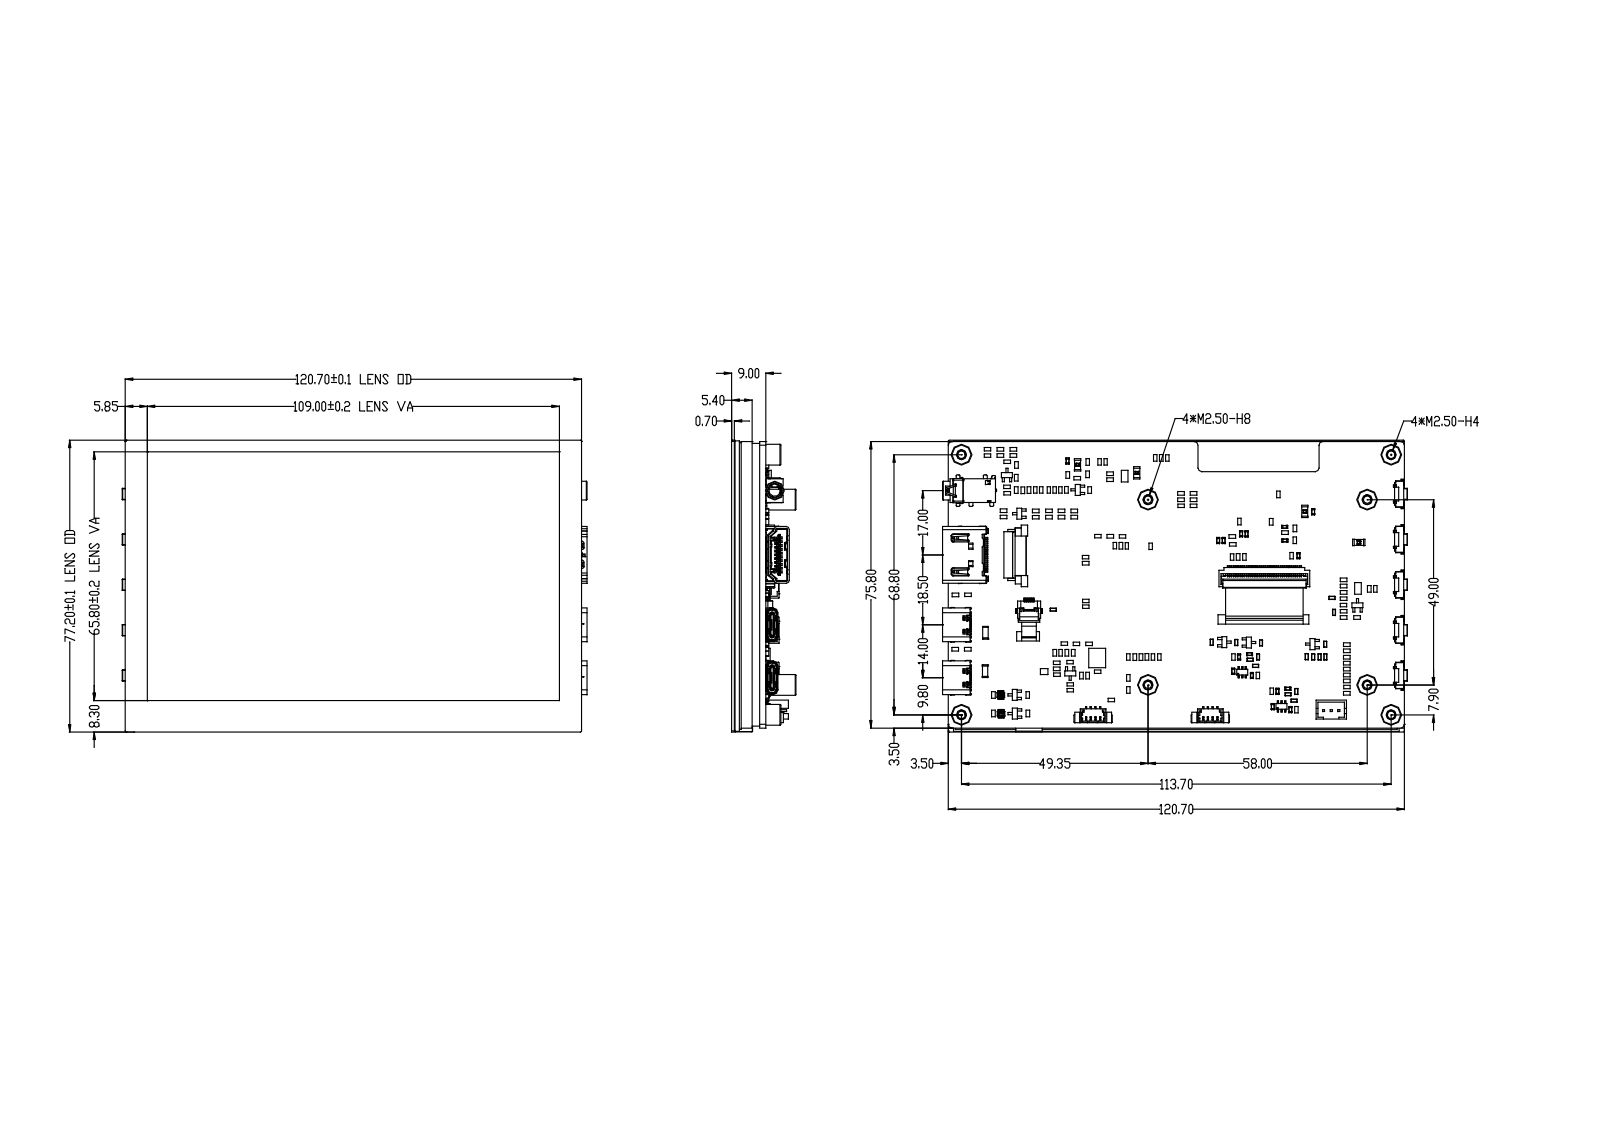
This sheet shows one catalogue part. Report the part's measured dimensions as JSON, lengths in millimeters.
{"part_name": "5INCH-1024X600-LCD; TG050-TP; 5INCH-1024X600-LCD_TP_ASM; SMTSO-M2_5-4ET (+8 more)", "step_written_by": "CREO PARAMETRIC BY PTC INC, 2021063 (CONFIG_CONTROL_DESIGN)", "units": "millimeters", "bodies": {"solids": 307, "faces": 9747, "planar": 6862, "cylindrical": 2207, "other": 678}, "overall_size": [123, 77.2, 17], "volume_mm3": 66686, "surface_area_mm2": 76986, "round_holes": [[0.8, 13], [2.5, 8], [4.3, 8], [1, 5], [0.76, 4], [0.22, 2], [1.4, 2], [3.6, 1]], "round_bosses_or_shafts": [[0.6, 10], [5.5, 8], [4.19, 8], [0.5, 4], [1.3, 2], [0.71, 2], [5, 1]], "partial_cylinders_radius": [[0.1, 185], [0.2, 78], [0.15, 73], [0.25, 63], [0.3, 42], [0.4, 39], [0.5, 23], [0.35, 21]], "face_to_face_distances": [2, 5.4, 1.6, 3.6, 2.5, 1.95, 7, 3.4, 2.85, 4.85], "hole_center_spacings": [2.3, 2, 2.95, 3.35, 3.82, 5.78, 6.26, 8.05]}
